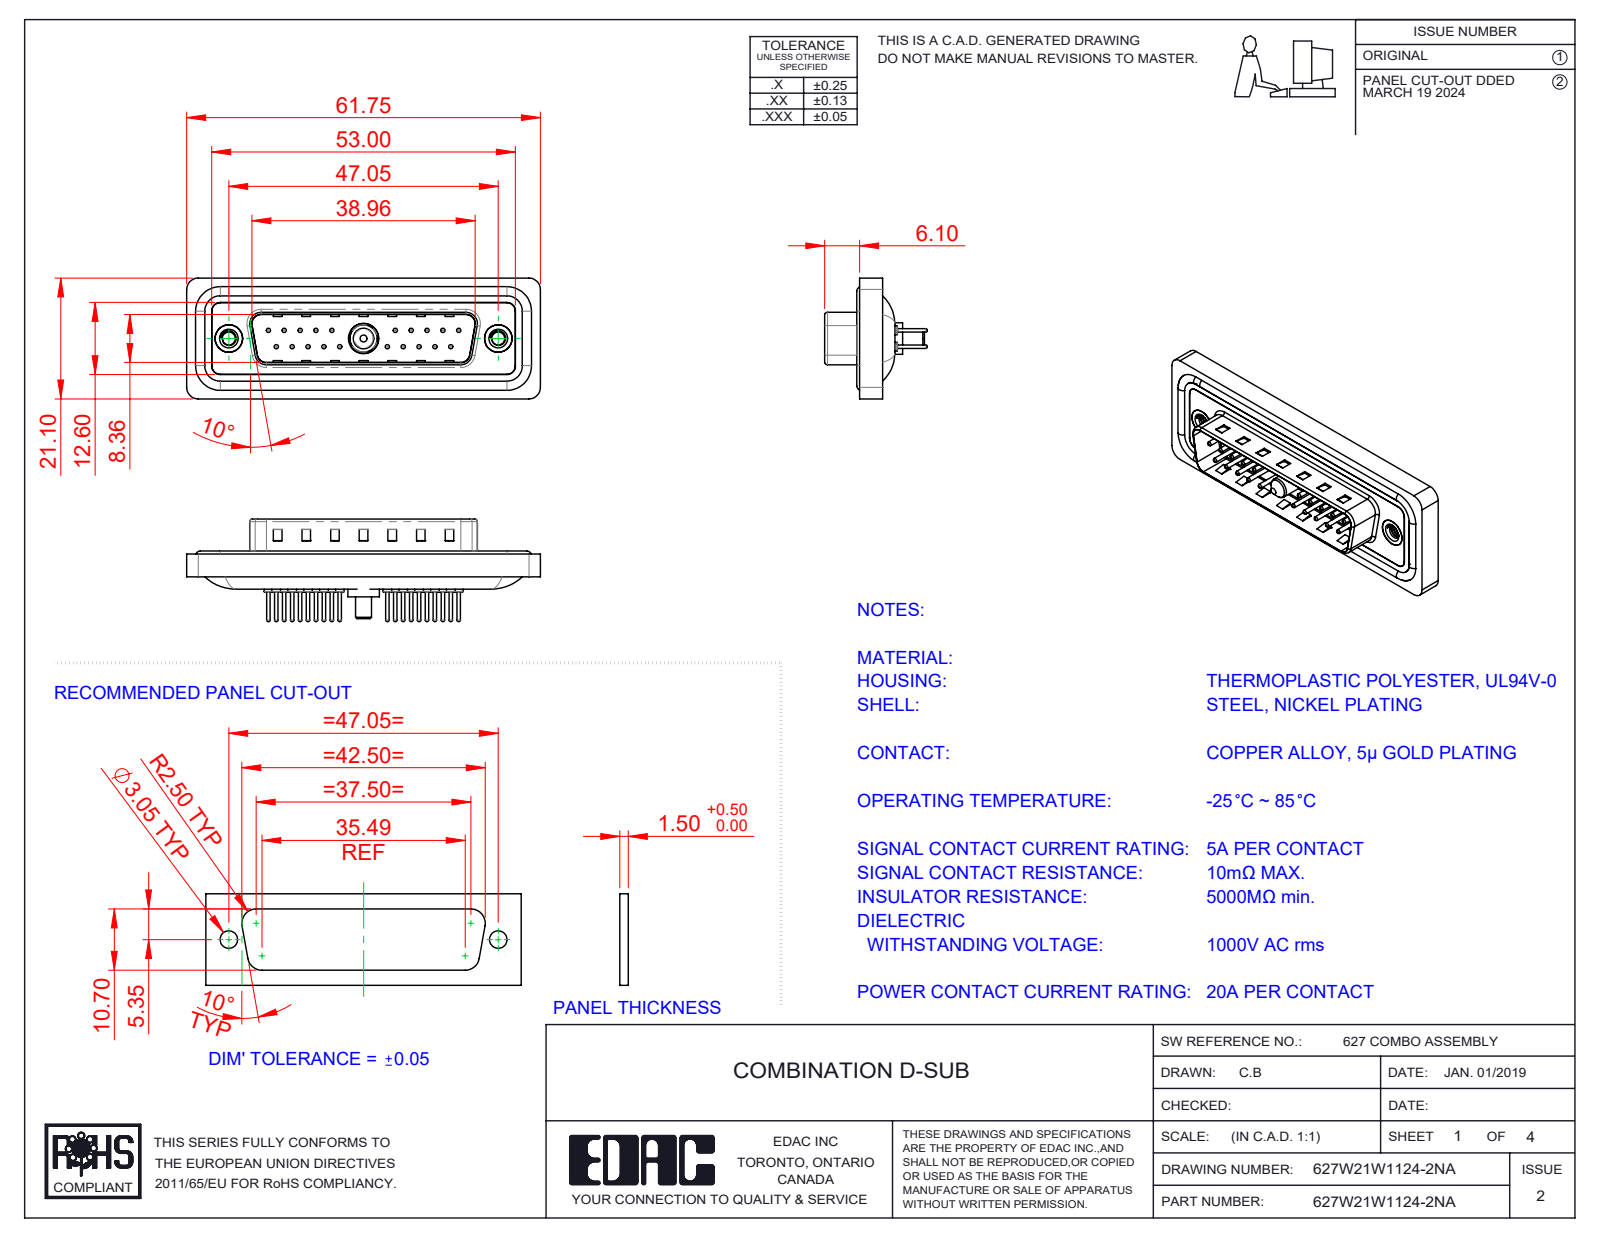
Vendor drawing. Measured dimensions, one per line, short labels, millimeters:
name: 627Combo Shell Front_25 Contacts; 627Combo Shell Rear_25 Contacts; 627Combo Waterproof Housing_25 Contacts; 627Combo Contact Row 1_24 (+5 more)
written by: SolidWorks 2023 (CONFIG_CONTROL_DESIGN)
unit: mm
bodies: 29 solids, 1260 faces (359 planar, 489 cylindrical, 412 other)
size: 61.75 × 21.1 × 17.9
volume: 7 199 mm³; area: 11 951 mm²
holes: 20× ⌀0.75, 20× ⌀1.6, 20× ⌀2, 2× ⌀2.26, 2× ⌀4, 2× ⌀4.8, 2× ⌀5, 1× ⌀4.85, 1× ⌀5.3
bosses: 20× ⌀1.5, 20× ⌀0.6, 4× ⌀1.6, 2× ⌀4.9, 1× ⌀5.5, 1× ⌀5.2, 1× ⌀4.75, 1× ⌀3.75
rounds: 22× R1.5, 18× R2, 8× R0.5, 8× R1.6, 4× R0.25, 4× R0.6, 4× R0.65, 4× R0.9
face distances: 0.4, 1.5, 1.1, 1.6, 0.5, 3.1, 2.9, 4.1, 0.82, 9.58
hole spacings: 3.16, 2.77, 5.54, 8.31, 5.04, 19.39, 20.97, 22.16
